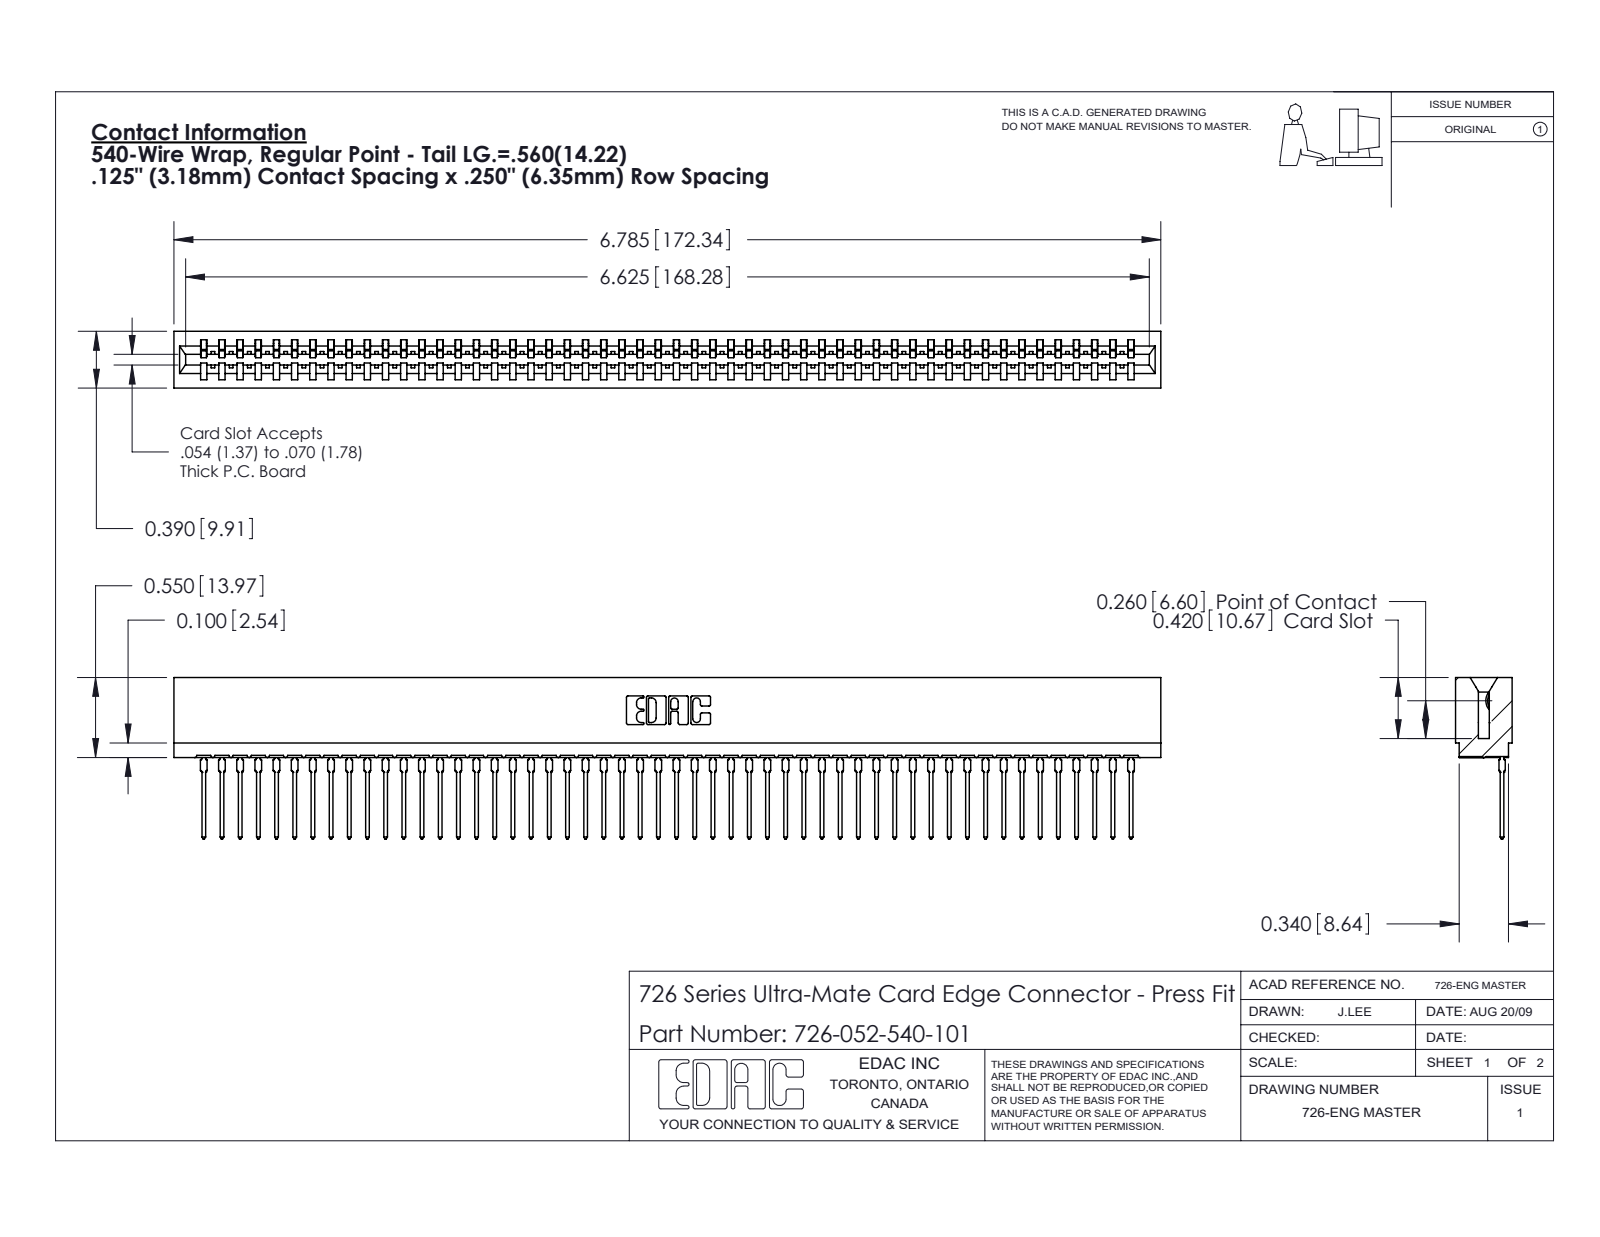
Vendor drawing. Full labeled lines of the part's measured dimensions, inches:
Part name (STEP PRODUCT): 746-292-001_540; 726 Part_.515 Slot Depth - 01; 726-052-540-101
STEP written by: SolidWorks 2020 (CONFIG_CONTROL_DESIGN)
Units: inches
Bodies: 53 solids, 5713 faces (3331 planar, 1030 cylindrical, 1352 other)
Overall size (bounding box): 6.785 × 1.109 × 0.39
Volume: 0.943 in³ · Surface area: 37.75 in²
Partial cylindrical surfaces — rounded edges, fillets, slot ends (radius × count): R0.021 ×104, R0.015 ×53, R0.01 ×22, R0.007 ×6, R0.031 ×6, R0.005 ×4, R0.011 ×4, R0.026 ×3
Main face-to-face distances: 0.057, 0.333, 0.39, 0.025, 0.307, 0.25, 0.083, 0.275, 0.365, 0.032
